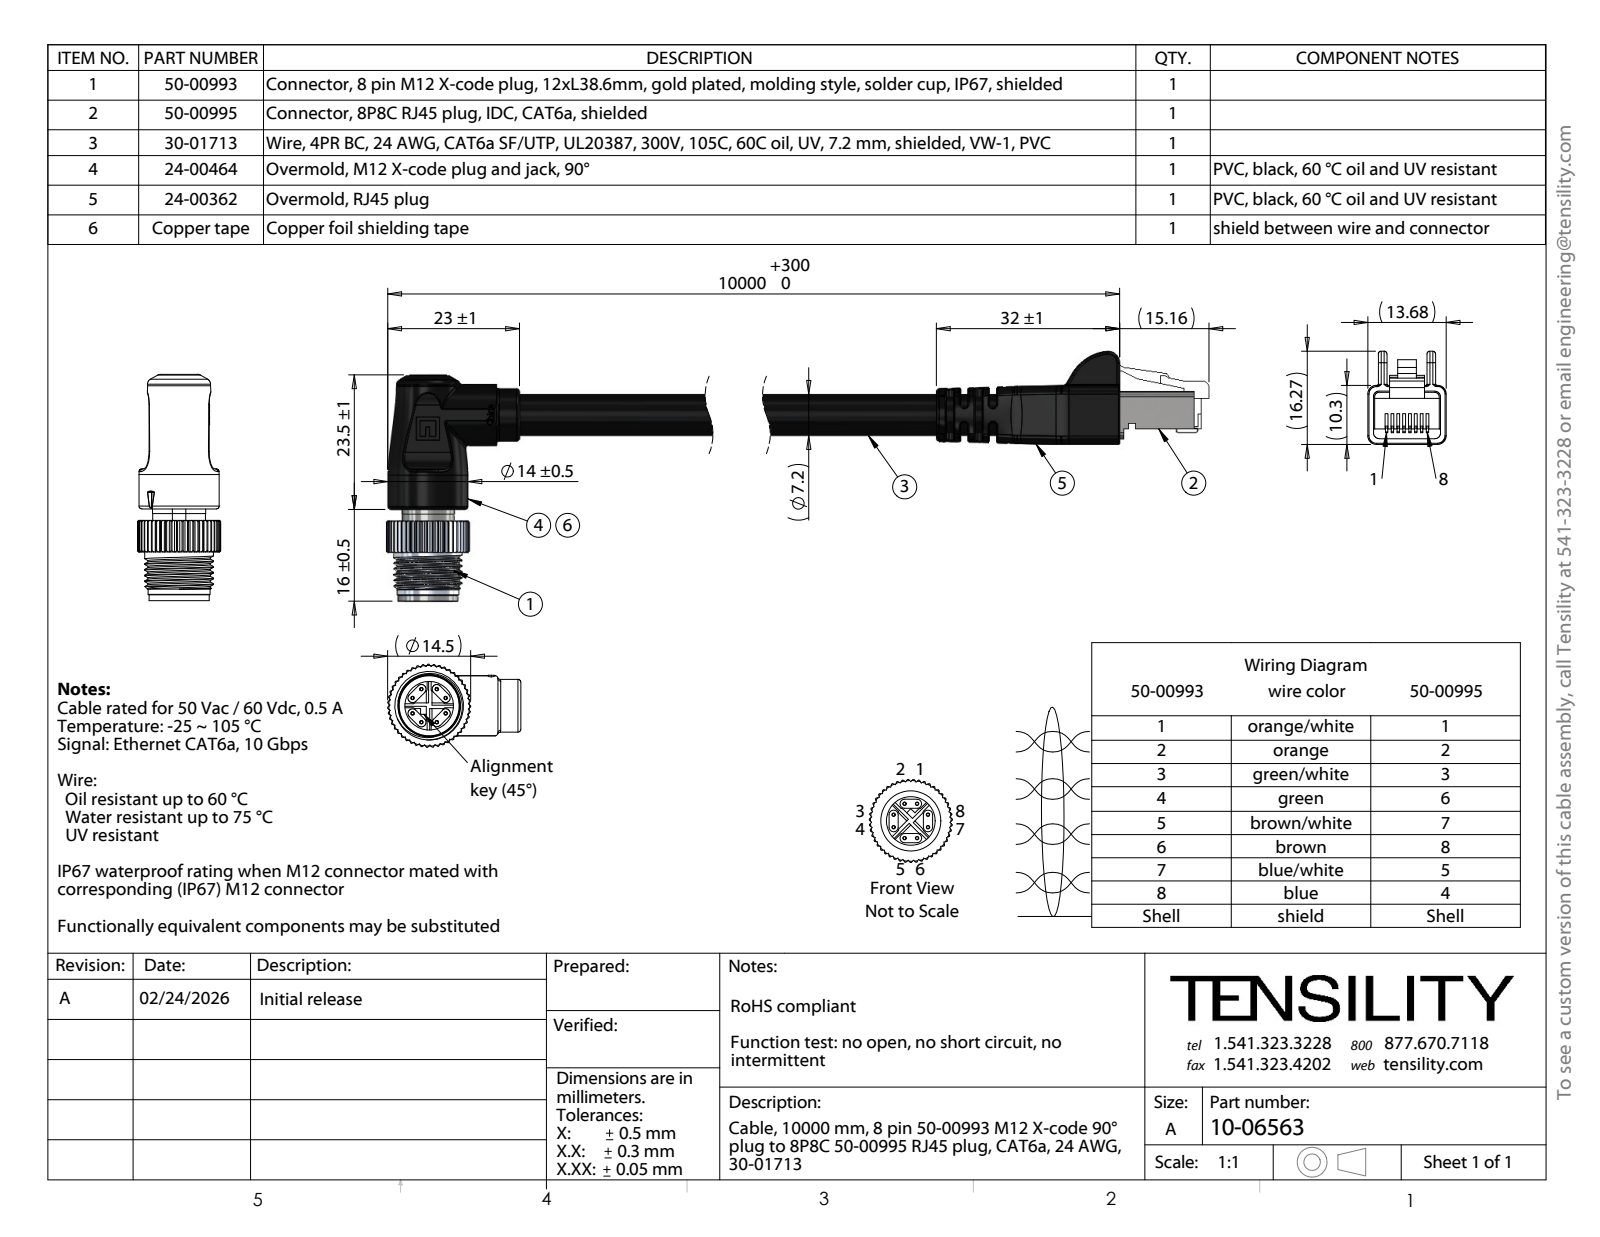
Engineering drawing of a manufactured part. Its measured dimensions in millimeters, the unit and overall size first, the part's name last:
Units: millimetres
Overall size (bounding box): 210.35 × 43.62 × 14.49
Round holes (diameter × count): ⌀0.2 ×56, ⌀0.6 ×8, ⌀1.2 ×8, ⌀2 ×1, ⌀2.5 ×1, ⌀5.03 ×1, ⌀5.25 ×1, ⌀5.65 ×1, ⌀5.75 ×1, ⌀7.5 ×1, ⌀8.5 ×1, ⌀9.07 ×1
Round bosses / shafts (diameter × count): ⌀1.4 ×8, ⌀1.15 ×8, ⌀1.05 ×8, ⌀0.8 ×8, ⌀9.2 ×2, ⌀14 ×1, ⌀12 ×1, ⌀11 ×1
Partial cylindrical surfaces — rounded edges, fillets, slot ends (radius × count): R0.5 ×14, R1 ×13, R0.1 ×12, R0.2 ×11, R0.8 ×10, R0.62 ×8, R1.5 ×8, R2.17 ×4
Main face-to-face distances: 0.5, 1, 0.99, 0.98, 2, 1.25, 5, 3.9, 3.75, 2.7
Hole centre spacings: 0.35, 1.61, 1.78, 0.41, 1.06, 1.43, 1.93, 2.48
Volume: 15 667 mm³ · Surface area: 49 597 mm²
Bodies: 95 solids, 2077 faces (843 planar, 677 cylindrical, 557 other)
Part name (STEP PRODUCT): 50-00993-02; 30-01713_blunt cut; 50-00993-04_默认; 50-00993_STEP (+7 more)
STEP written by: SolidWorks 2025 (CONFIG_CONTROL_DESIGN)
